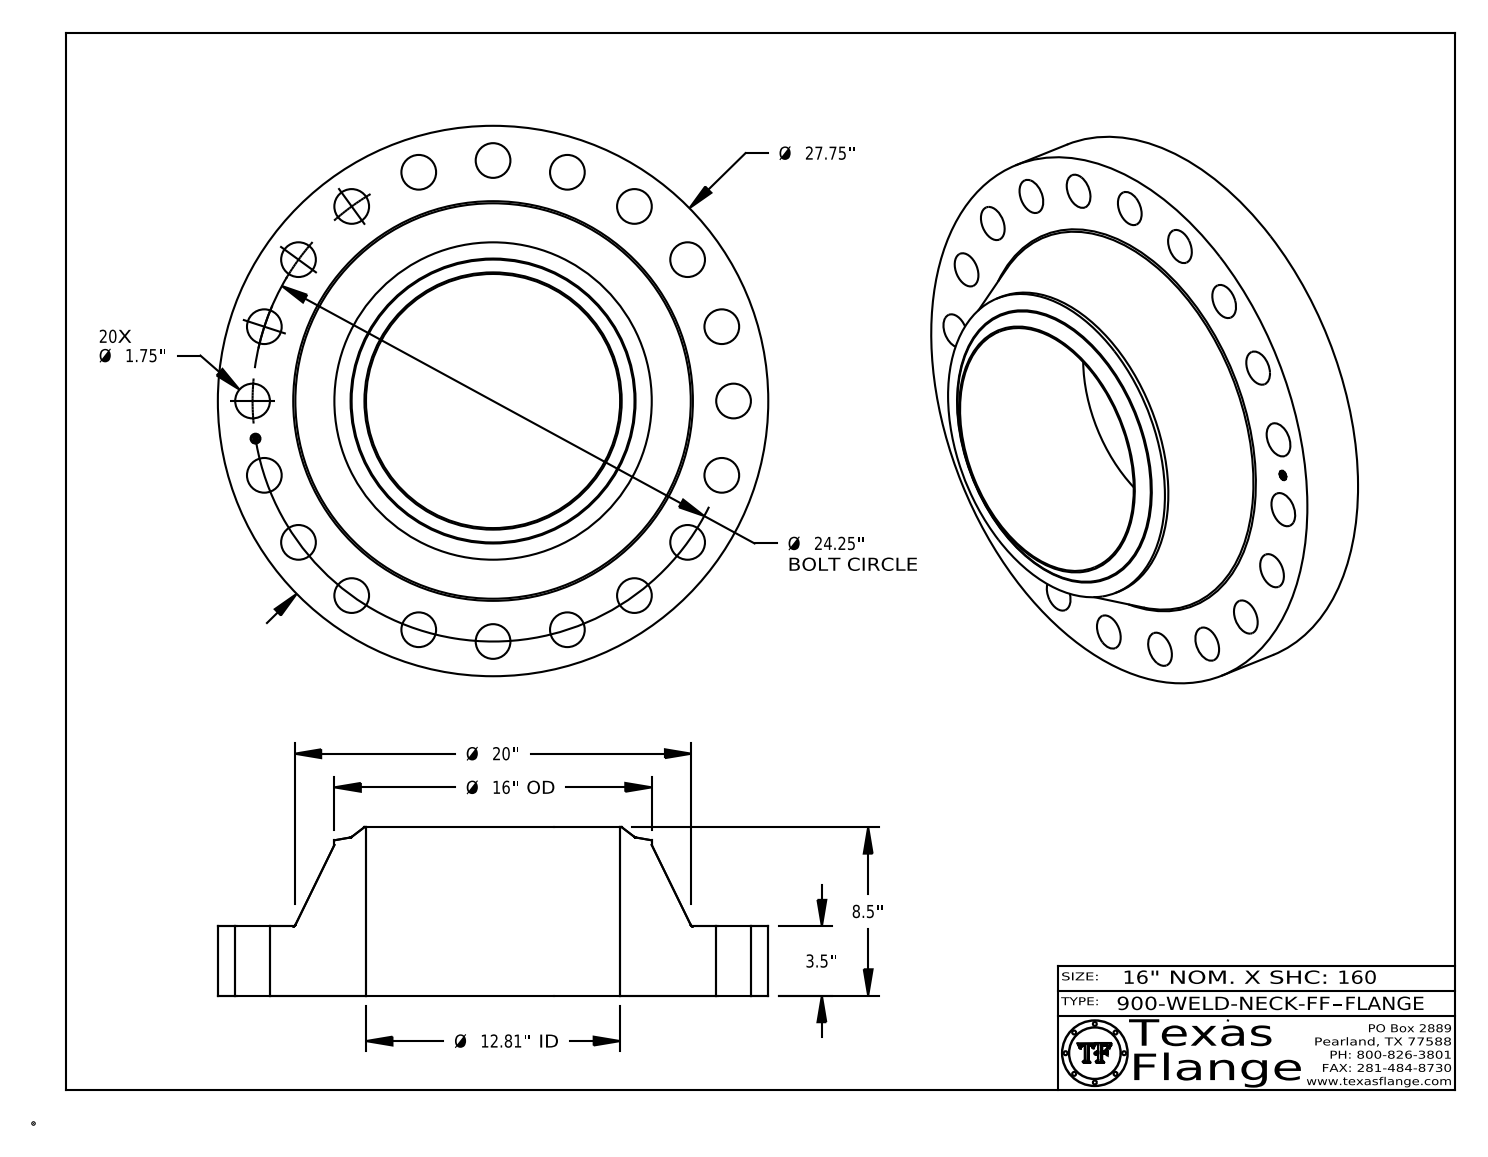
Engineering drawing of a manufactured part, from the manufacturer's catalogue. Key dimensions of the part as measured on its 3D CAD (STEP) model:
Part name (STEP PRODUCT): 900-WELD-NECK-FF
STEP written by: CATIA V5 STEP AP214 (AUTOMOTIVE_DESIGN)
Units: inches
Bodies: 1 solid, 444 faces (368 planar, 66 cylindrical, 10 other)
Overall size (bounding box): 27.75 × 27.75 × 8.5
Volume: 2 050 in³ · Surface area: 2 052 in²
Round holes (diameter × count): ⌀1.75 ×20, ⌀0.495 ×1, ⌀12.812 ×1
Round bosses / shafts (diameter × count): ⌀0.03 ×8, ⌀27.75 ×1, ⌀16 ×1, ⌀0.39 ×1
Main face-to-face distances: 3.5, 8.5, 5, 3.485, 0.015, 5.015, 0.148, 0.145, 0.027, 0.096
Hole centre spacings: 17.147, 23.063, 19.619, 12.125, 3.794, 7.494, 11.009, 14.254
